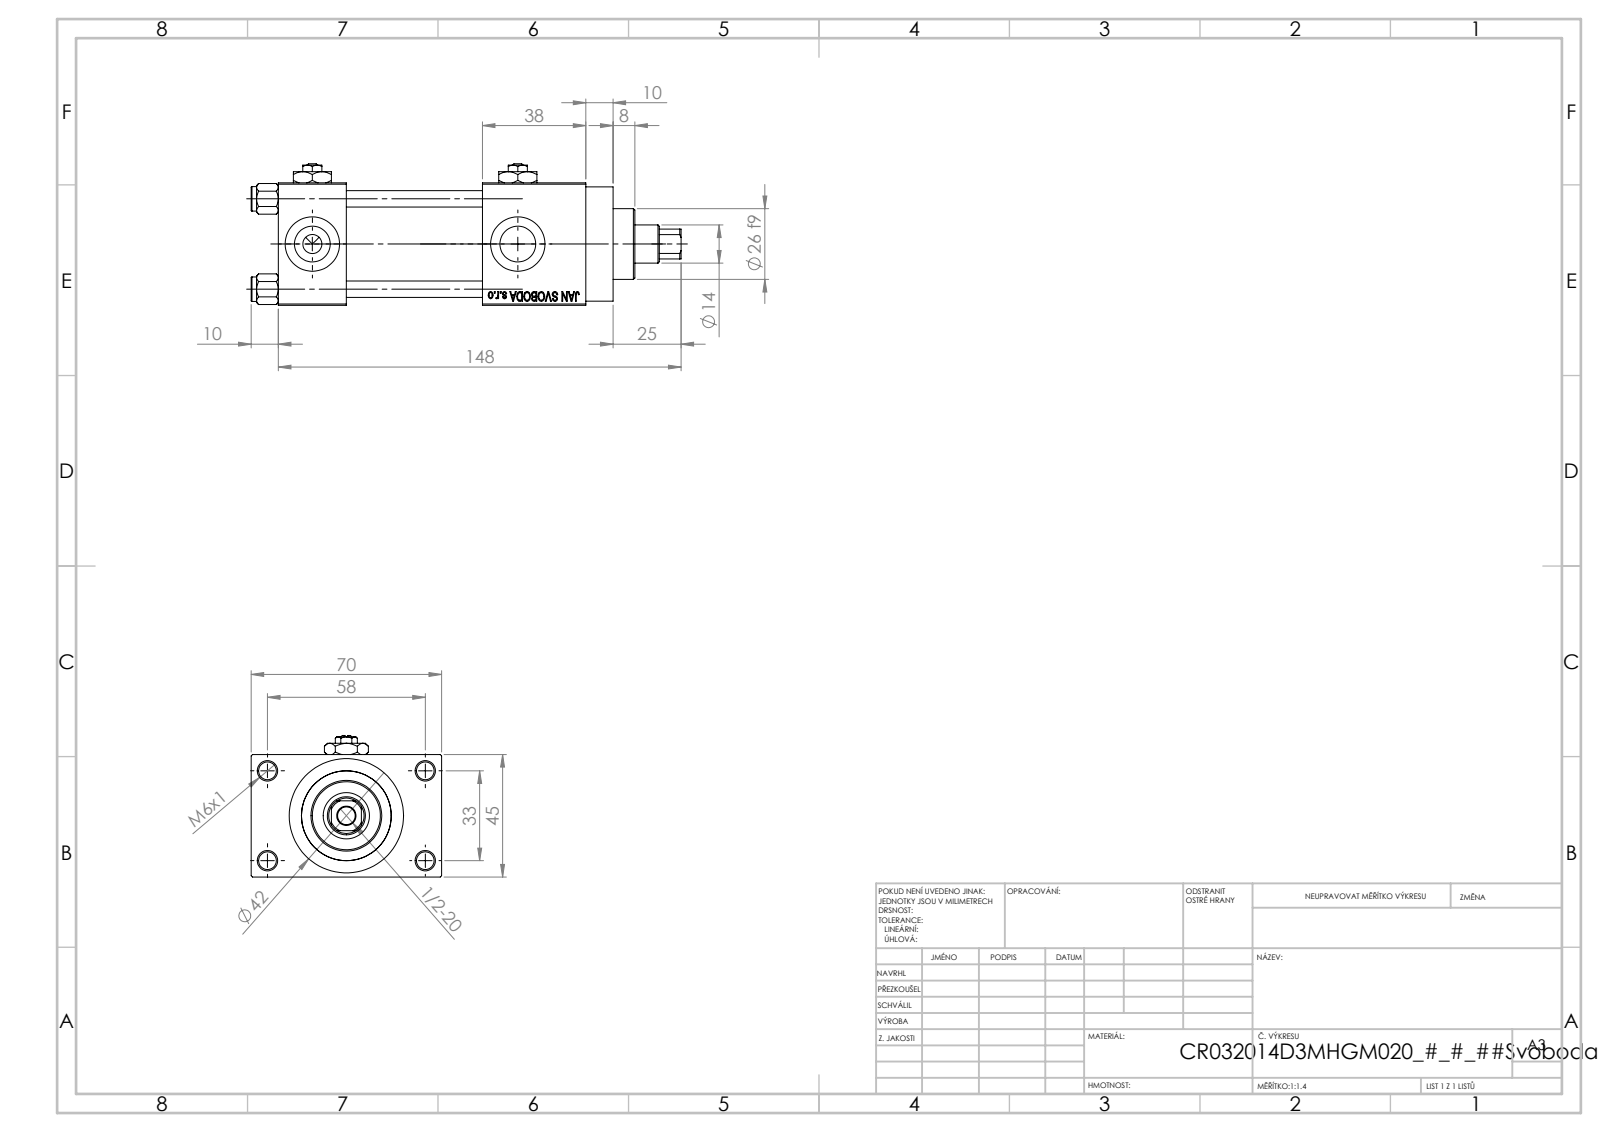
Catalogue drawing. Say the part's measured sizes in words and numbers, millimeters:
The part is named "NUT_M5_D; V215_VC_A; V215CR_VCP_D; V215CR_D_Body (+2 more)". Its 3-D file was written by "SolidWorks 2019 (CONFIG_CONTROL_DESIGN)". It is 13 solids with 1201 faces: 542 planar, 99 cylindrical and 560 other. Overall it measures 158 by 70 by 52 millimeters. Its volume is 229 076 cubic millimeters and its surface area 77 129 square millimeters. Round holes: 5 of diameter 6.5, 4 of diameter 6, 4 of diameter 13.16, 4 of diameter 20, 3 of diameter 7, 1 of diameter 14, 1 of diameter 17, 1 of diameter 24, 1 of diameter 32, 1 of diameter 33. Round bosses or shafts: 4 of diameter 9, 1 of diameter 42, 1 of diameter 38, 1 of diameter 26. Partial cylindrical surfaces (rounded edges, fillets, slot ends): 1 of radius 6.5. The main face-to-face distances are 45, 25, 50, 12.5, 75, 57.5, 88, 38, 113, 70. The hole center spacings are 12.4, 23.48, 33.2, 33.37, 35.35, 45.6, 56.35, 33.
